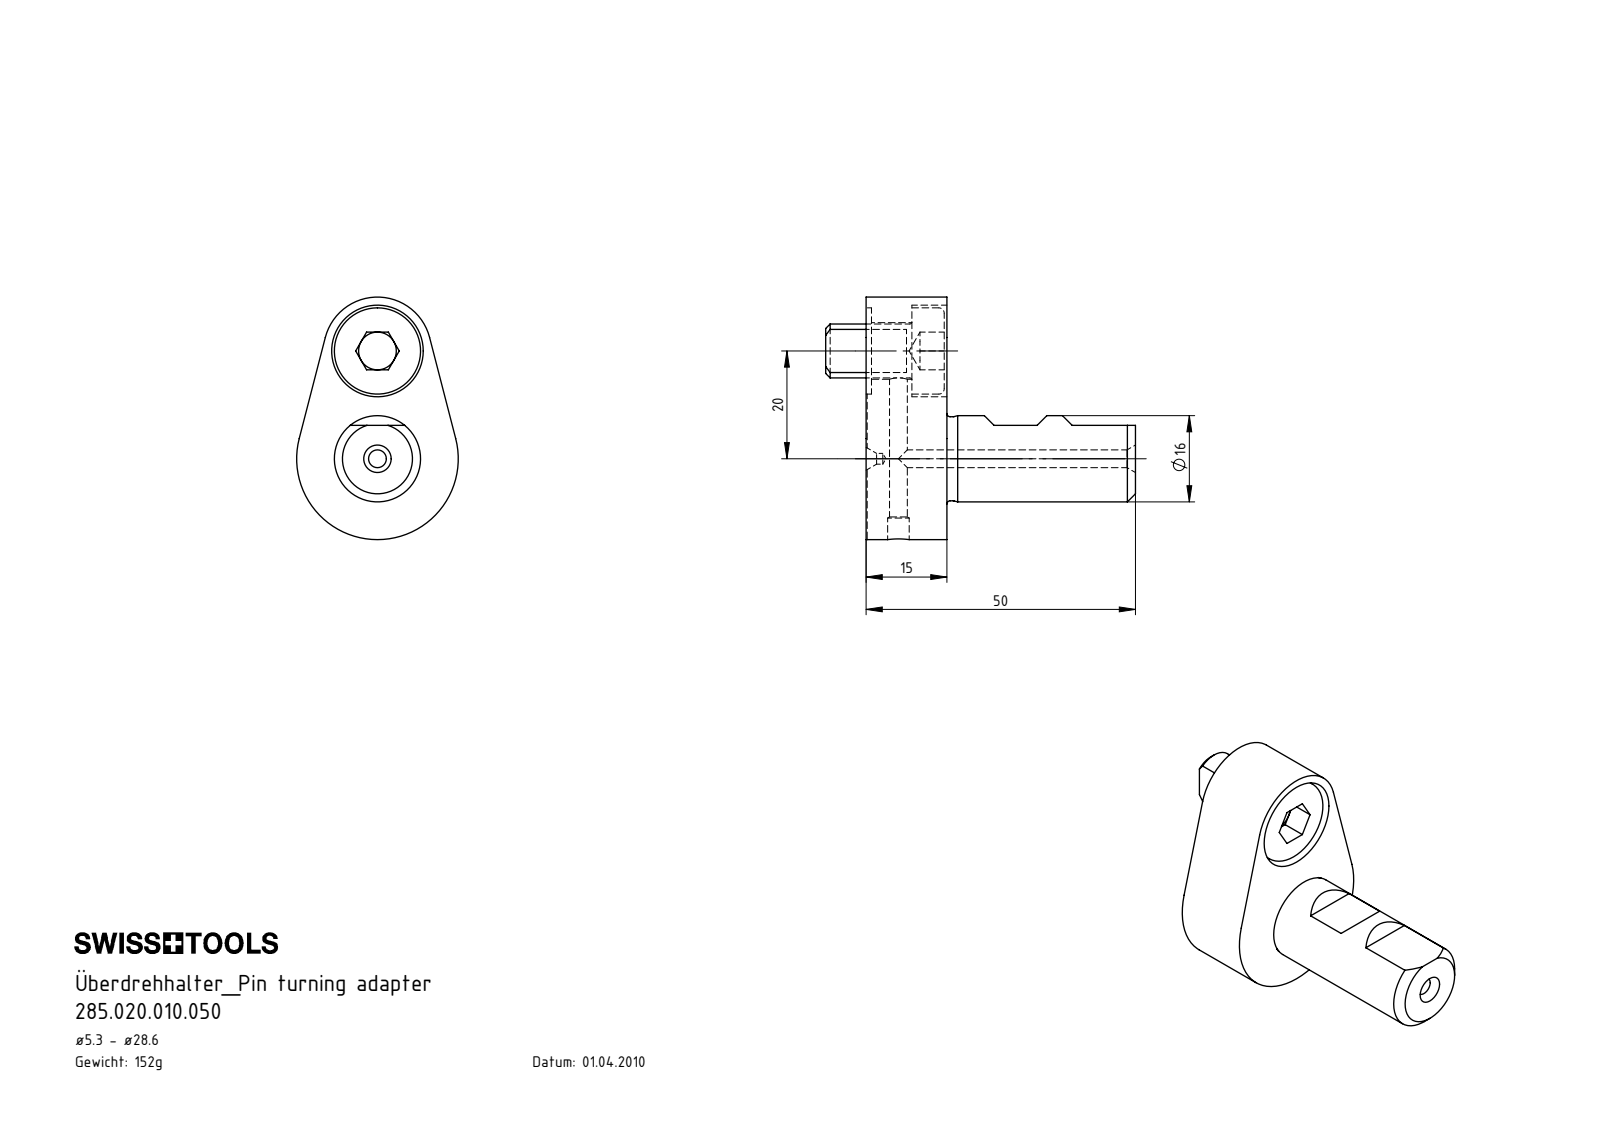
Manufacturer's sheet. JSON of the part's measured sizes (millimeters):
{"part_name": "UH1-U20.K01.015; HS0-A32.K11.027; CCMT060204; WCA-ER2.001.006_A (+3 more)", "step_written_by": "SolidWorks 2017 (CONFIG_CONTROL_DESIGN)", "units": "millimeters", "bodies": {"solids": 5, "faces": 208, "planar": 67, "cylindrical": 61, "other": 80}, "overall_size": [76, 45, 30], "volume_mm3": 24761, "surface_area_mm2": 10341, "round_holes": [[3.3, 2], [2, 1], [2.05, 1], [2.8, 1], [3, 1], [3.85, 1], [4, 1], [8.2, 1], [10.5, 1], [17, 1]], "round_bosses_or_shafts": [[16, 2], [15.6, 1], [10, 1], [3.4, 1], [2.5, 1]], "partial_cylinders_radius": [[0.21, 6], [0.36, 5], [0.36, 1], [1.5, 1], [1.8, 1], [2, 1], [10, 1], [15, 1]], "face_to_face_distances": [15, 8.5, 7.5, 14, 6.5, 1, 6, 0.5, 11, 35], "hole_center_spacings": [20]}
